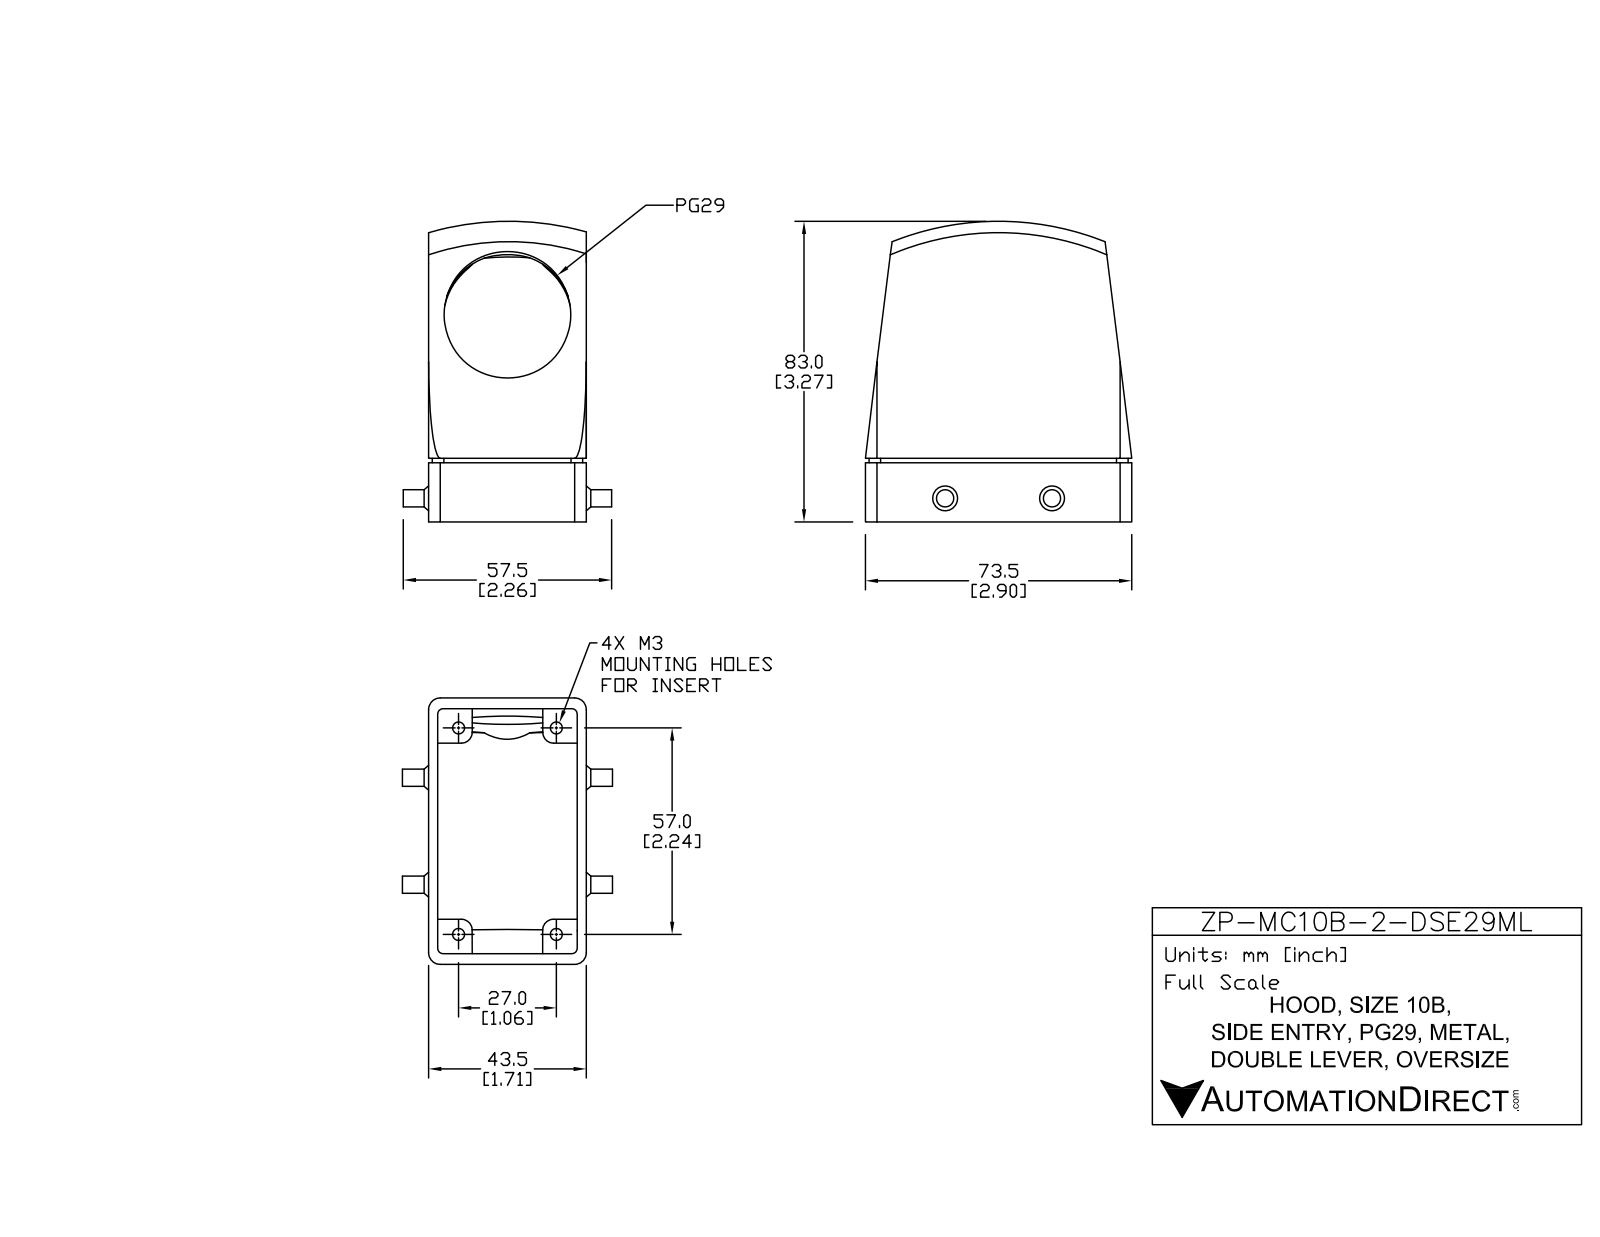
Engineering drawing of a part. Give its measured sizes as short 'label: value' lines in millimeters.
name: ZP-MC10B-2-DSE29ML
written by: SolidWorks 2011 (AUTOMOTIVE_DESIGN)
unit: mm
bodies: 5 solids, 100 faces (56 planar, 34 cylindrical, 10 other)
size: 77.55 × 73.5 × 58
volume: 55 441 mm³; area: 42 669 mm²
holes: 4× ⌀3.5, 1× ⌀35.5
bosses: 2× ⌀4.75
rounds: 8× R3.2, 4× R0.7, 4× R3
face distances: 2.5, 41, 43.5, 38.5, 9.5, 58.08, 2.96, 12.46, 61.04, 70.54
hole spacings: 28.96, 59, 65.72
